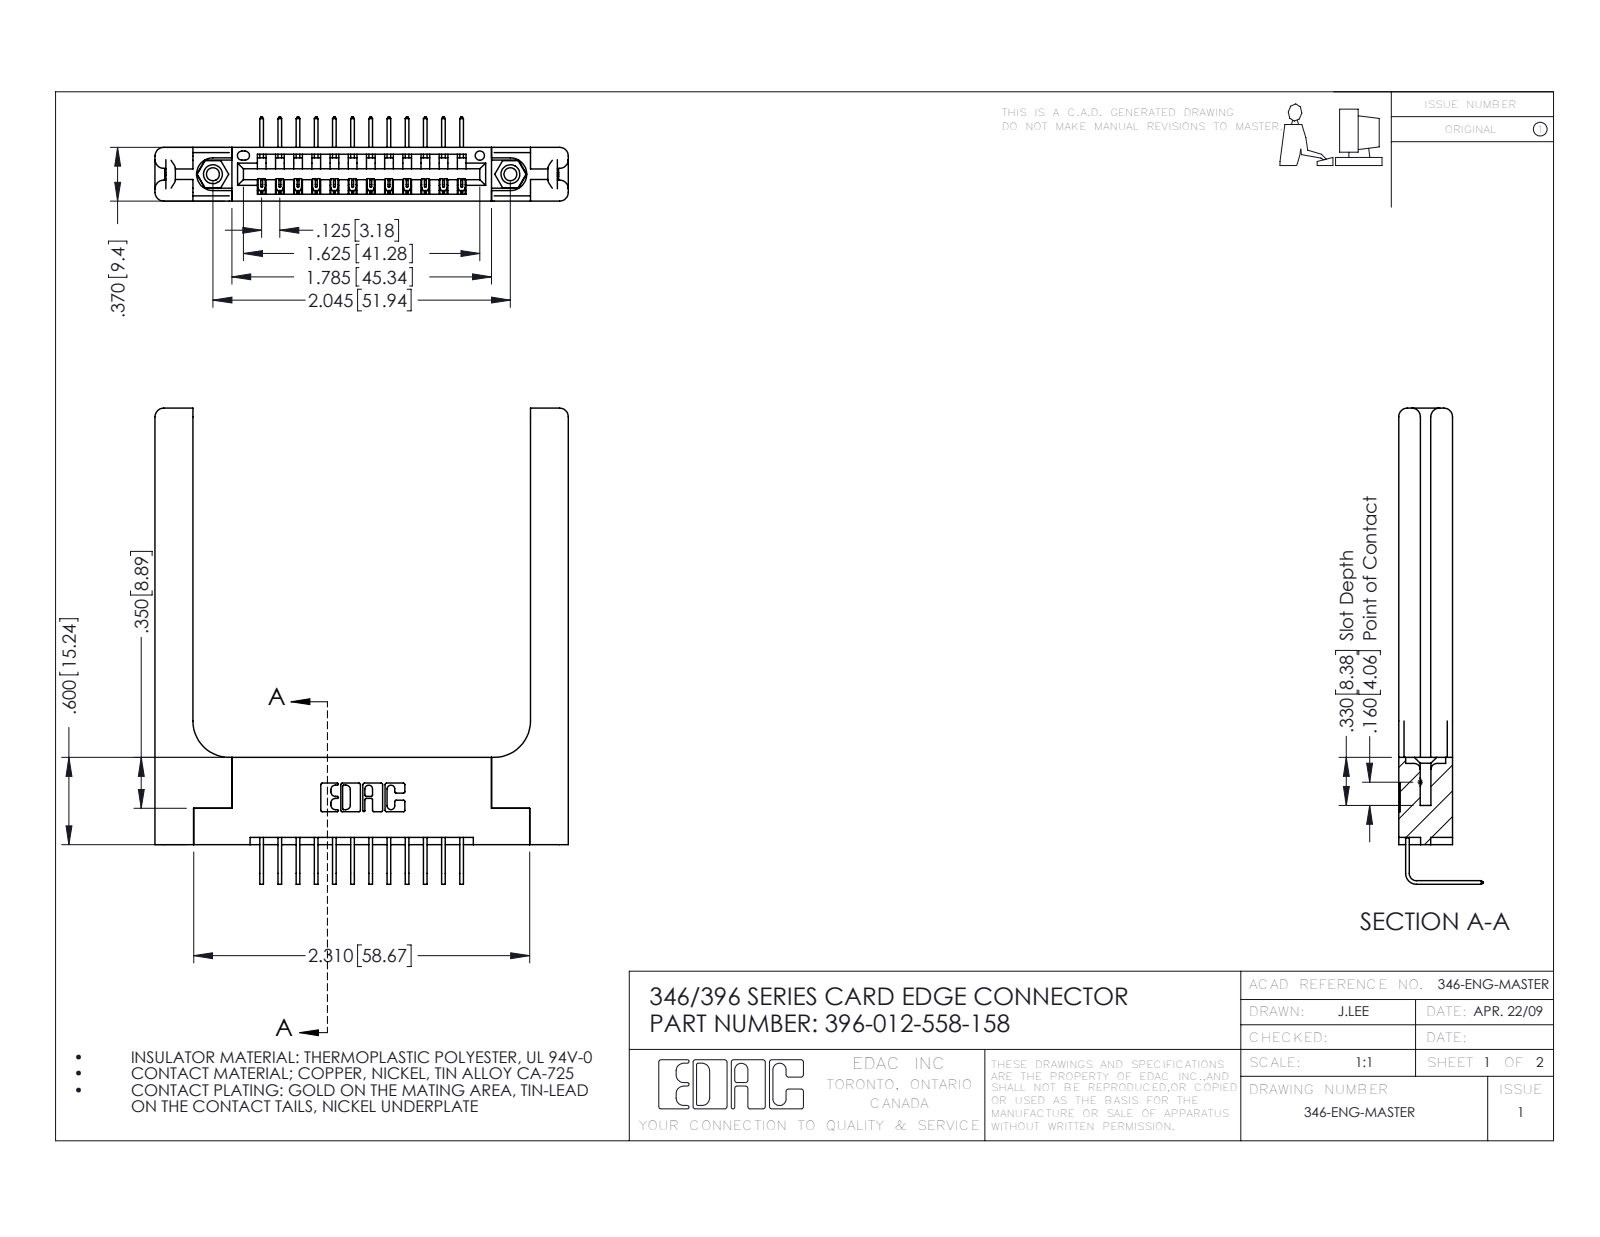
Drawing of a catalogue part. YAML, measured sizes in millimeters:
part_name: "396-012-558-158; 345-292-001_558 Tail - 2; 345-250-001_345-250-001-102; 346 Part_Flush Mounting Lugs - 0.156 Dia-TH (+1 more)"
step_written_by: "SolidWorks 2016 (CONFIG_CONTROL_DESIGN)"
units: millimeters
bodies: {solids: 17, faces: 1098, planar: 728, cylindrical: 310, other: 60}
overall_size: [83.1, 72.2, 14.7]
volume: 14300
surface_area: 13510
round_holes:
  - {diameter: 2.3, count: 2}
  - {diameter: 3.2, count: 2}
  - {diameter: 4, count: 2}
  - {diameter: 1.6, count: 1}
round_bosses_or_shafts:
  - {diameter: 3.9, count: 2}
partial_cylinders:
  - {radius: 0.2, count: 24}
  - {radius: 0.3, count: 22}
  - {radius: 1.5, count: 16}
  - {radius: 0.2, count: 6}
  - {radius: 0.8, count: 6}
  - {radius: 0.7, count: 3}
  - {radius: 0.8, count: 2}
  - {radius: 0.8, count: 2}
face_to_face_distances: [9.4, 3.8, 1.8, 3.8, 8.2, 5.6, 1.2, 6.4, 2.6, 4.4]
hole_center_spacings: [6.2, 46.7, 51.9]
